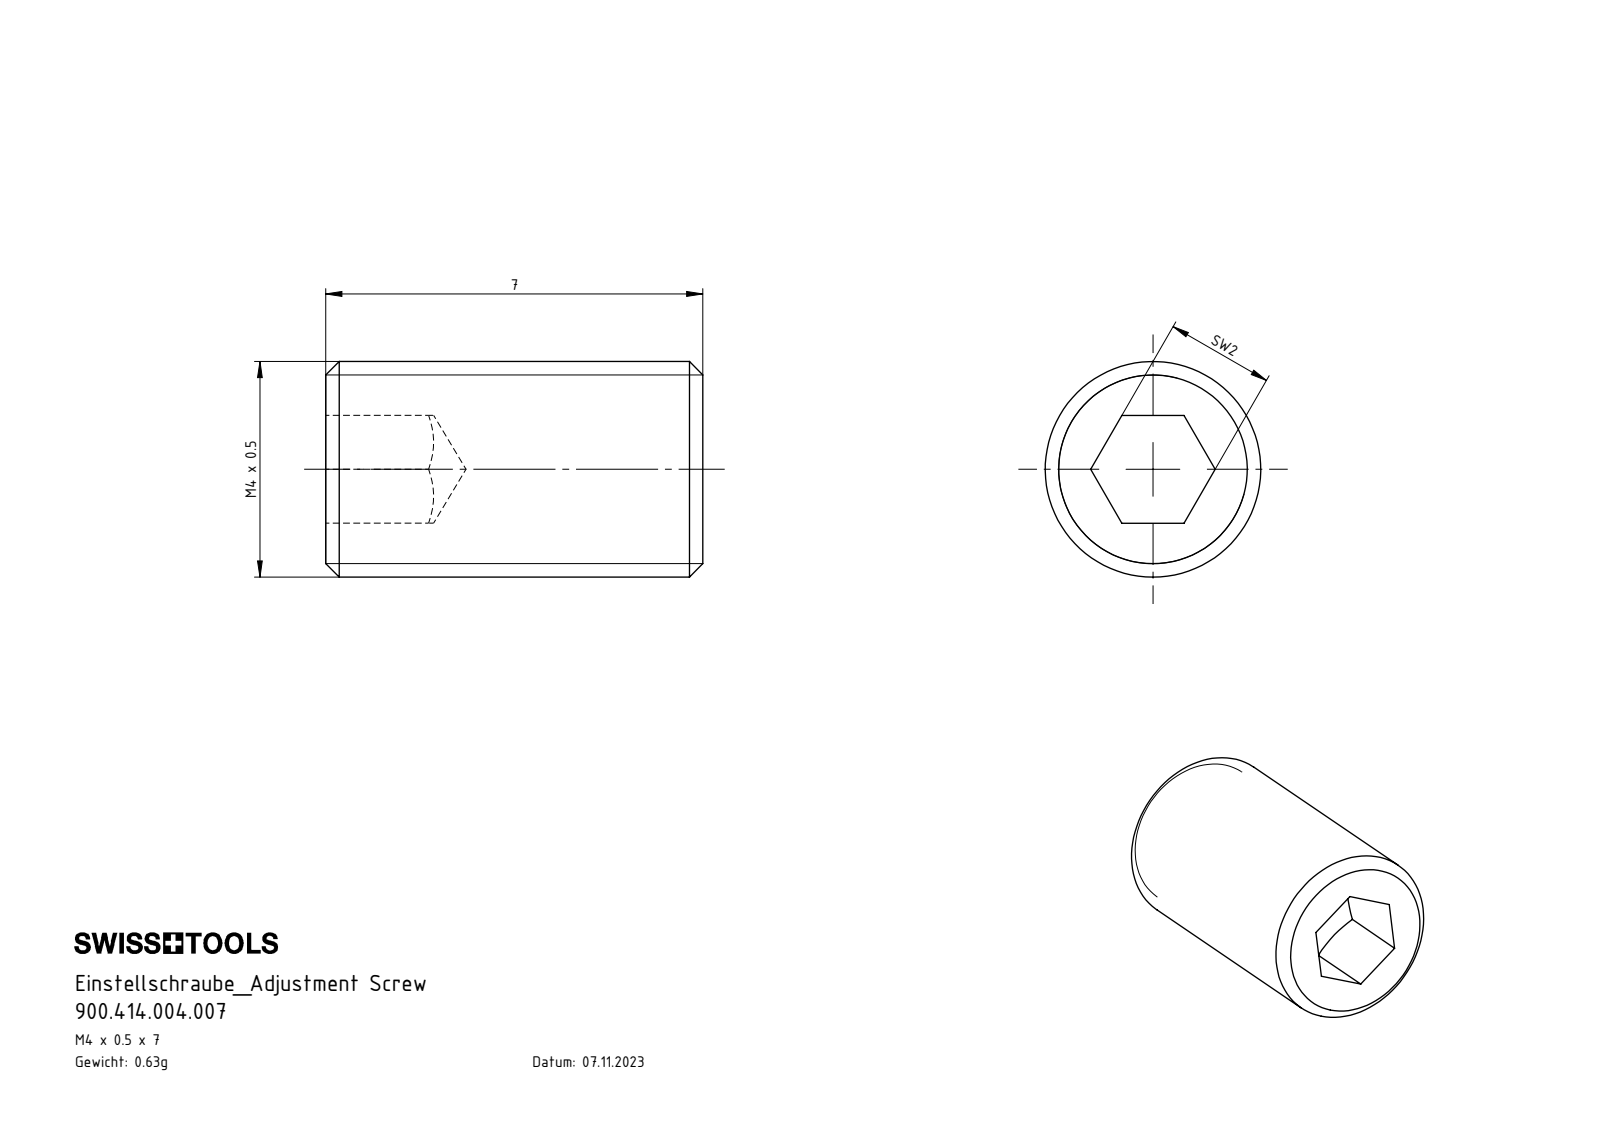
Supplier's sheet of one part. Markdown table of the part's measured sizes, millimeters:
| quantity | value |
| --- | --- |
| part name | 900.414.004.007 |
| STEP written by | SolidWorks 2022 (AUTOMOTIVE_DESIGN) |
| units | millimeters |
| bodies | 1 solid, 16 faces (8 planar, 2 cylindrical, 6 other) |
| overall size | 7 × 4 × 4 |
| volume | 80 mm³ |
| surface area | 123 mm² |
| round bosses / shafts (diameter × count) | 4 × 1 |
| main face-to-face distances | 2, 7 |
